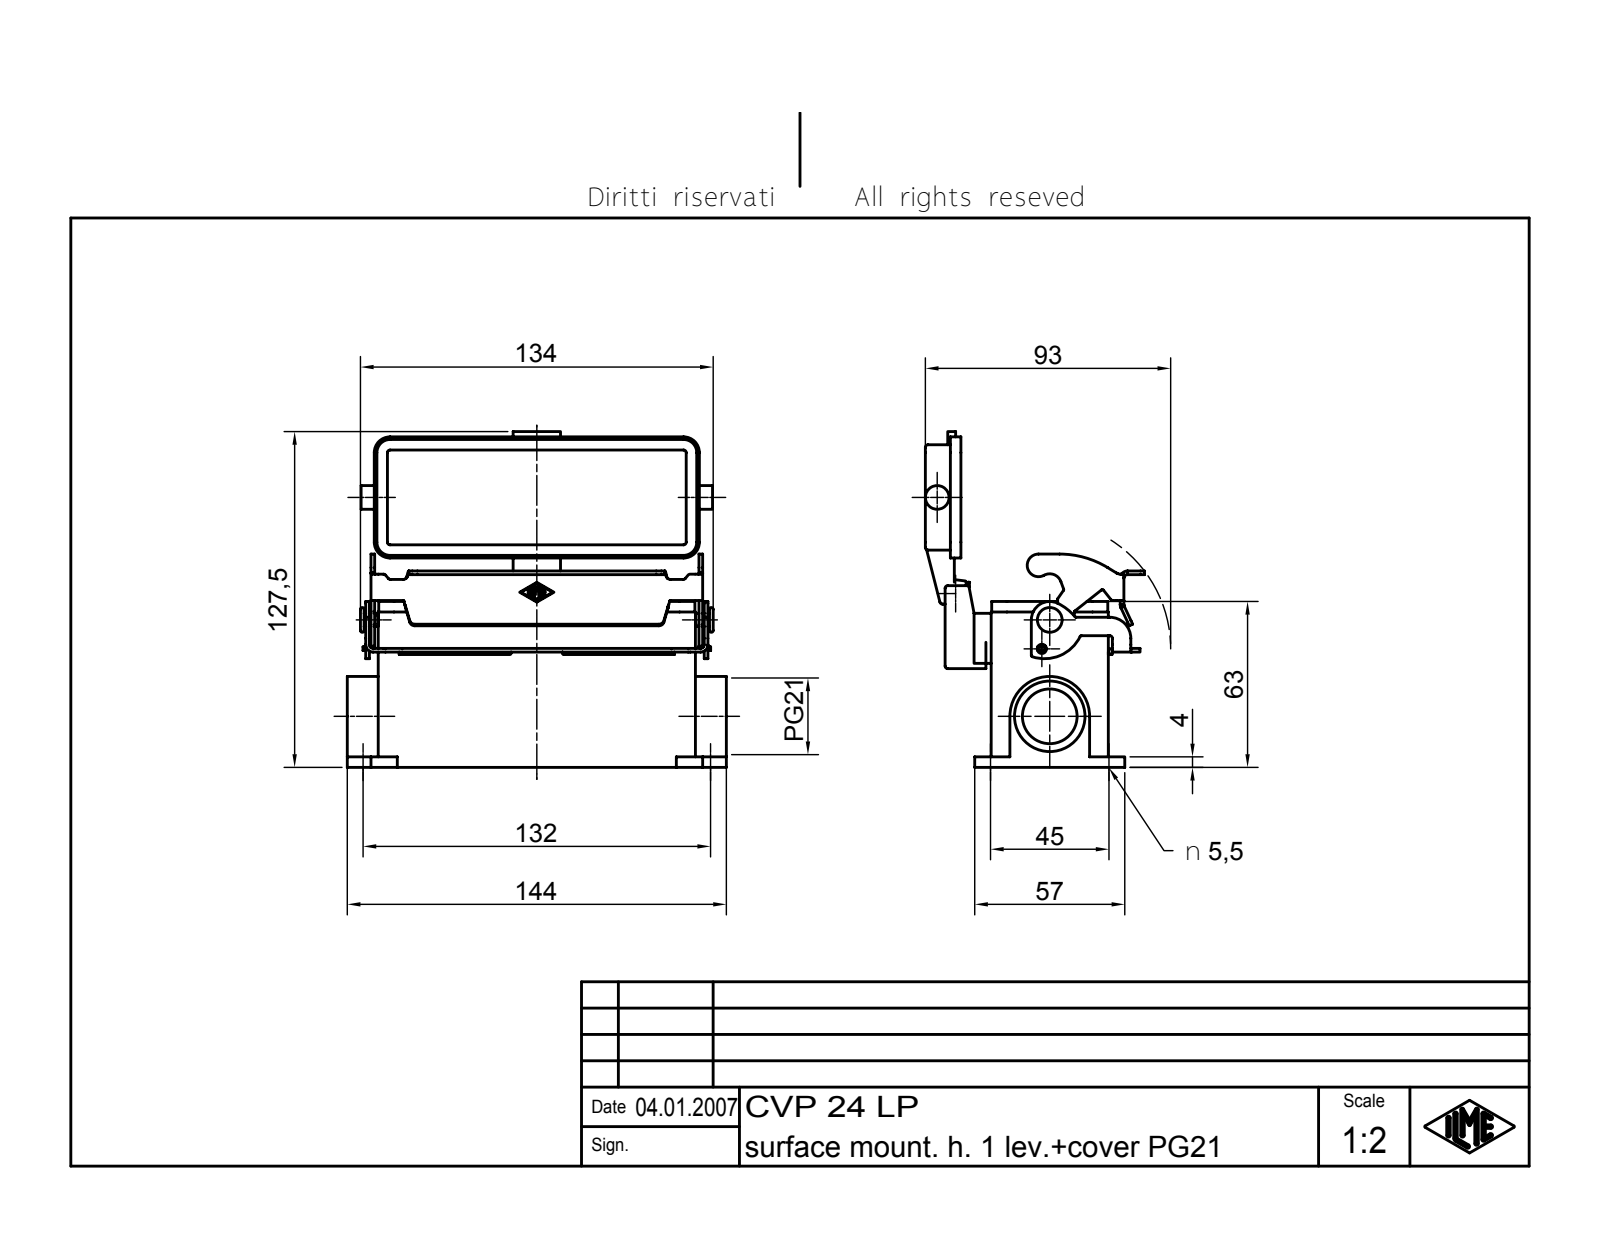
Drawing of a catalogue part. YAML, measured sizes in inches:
part_name: "CVP 24 LP"
step_written_by: "Autodesk Inventor 7 (AUTOMOTIVE_DESIGN)"
units: inches
bodies: {solids: 4, faces: 590, planar: 232, cylindrical: 193, other: 165}
overall_size: [5.669, 5.02, 3.277]
volume: 9.441
surface_area: 147.7
round_holes:
  - {diameter: 0.217, count: 4}
  - {diameter: 0.138, count: 1}
  - {diameter: 0.157, count: 1}
  - {diameter: 0.818, count: 1}
  - {diameter: 1.054, count: 1}
round_bosses_or_shafts:
  - {diameter: 0.197, count: 2}
  - {diameter: 0.354, count: 1}
  - {diameter: 0.276, count: 1}
  - {diameter: 0.126, count: 1}
  - {diameter: 0.118, count: 1}
partial_cylinders:
  - {radius: 0.039, count: 32}
  - {radius: 0.01, count: 15}
  - {radius: 0.02, count: 10}
  - {radius: 0.059, count: 9}
  - {radius: 0.236, count: 8}
  - {radius: 0.079, count: 7}
  - {radius: 0.055, count: 6}
  - {radius: 0.11, count: 6}
face_to_face_distances: [0.157, 1.594, 1.752, 1.437, 0.925, 0.079, 2.736, 2.579, 1.142, 0.984]
hole_center_spacings: [1.772, 5.197, 5.491, 1.015]
